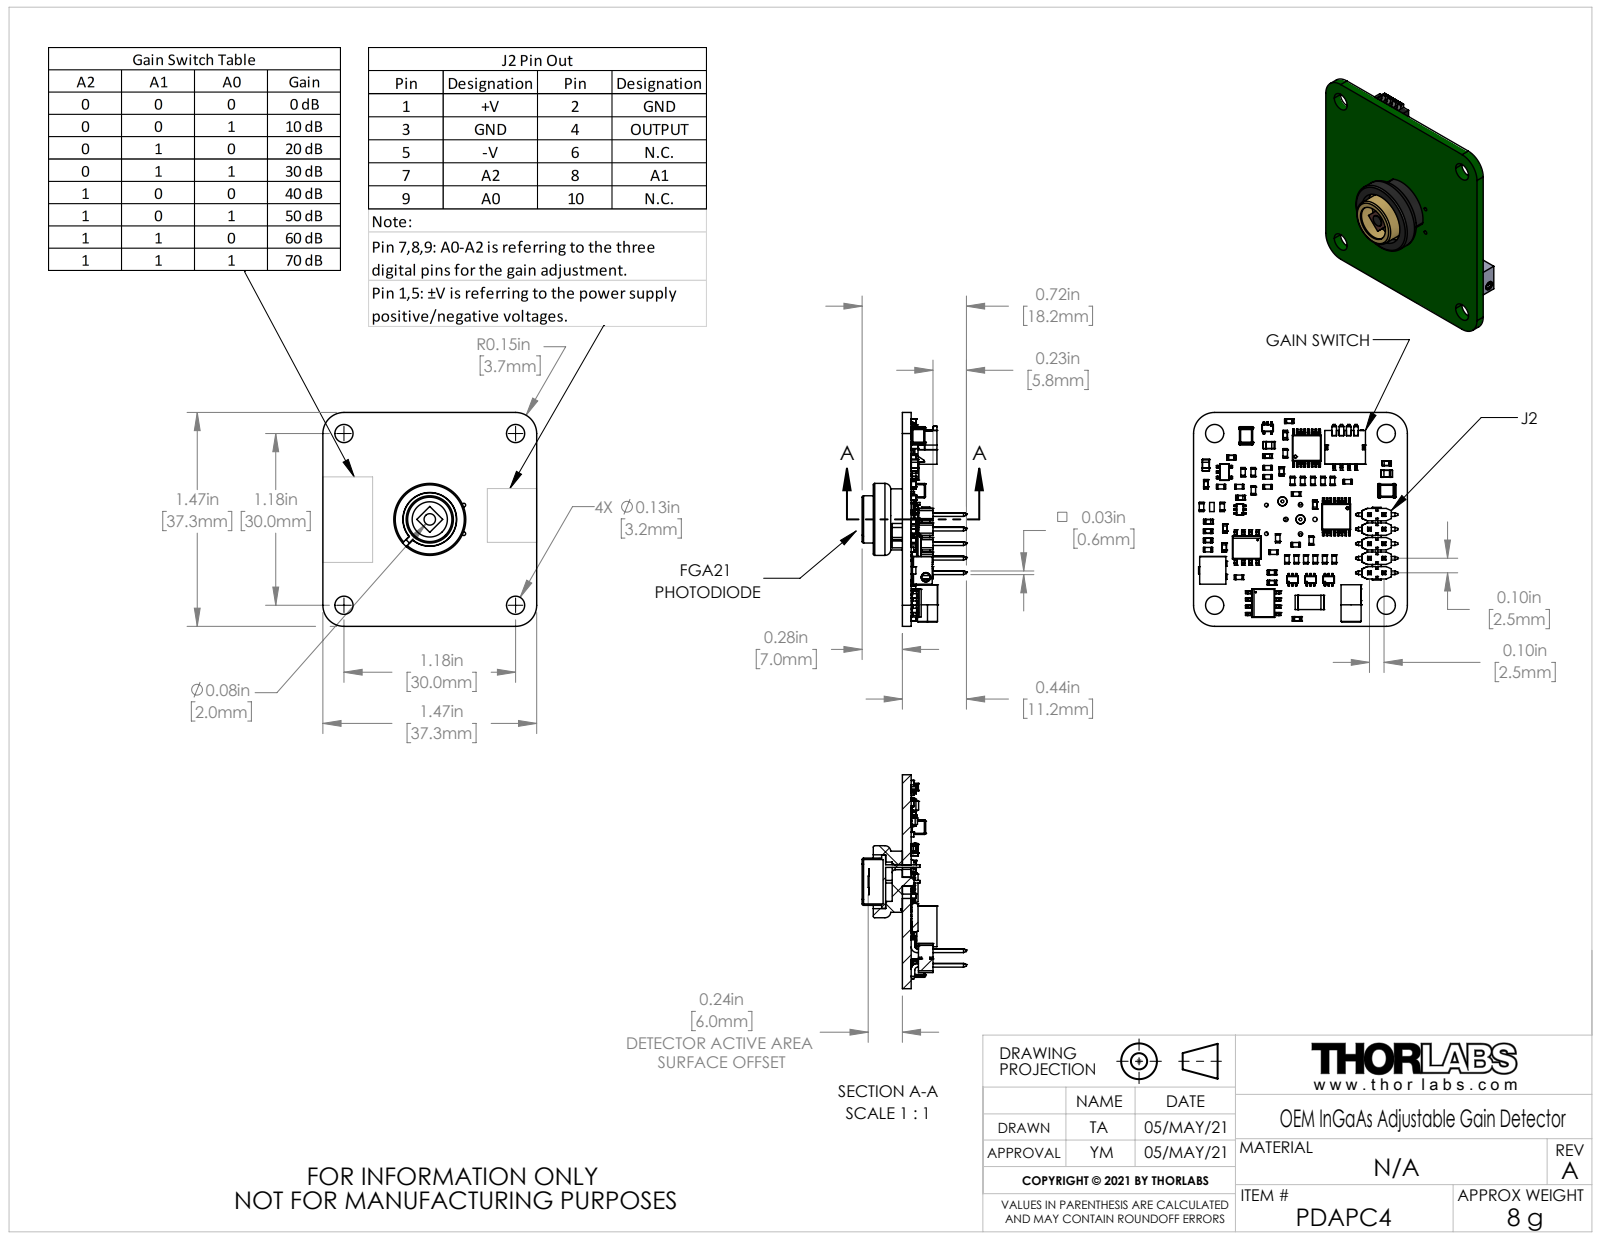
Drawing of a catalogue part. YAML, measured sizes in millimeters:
part_name: "TTN239793-E0W"
step_written_by: "SolidWorks 2018 (AUTOMOTIVE_DESIGN)"
units: millimeters
bodies: {solids: 76, faces: 4206, planar: 2902, cylindrical: 1038, other: 266}
overall_size: [37.3, 37.3, 18.2]
volume: 3160
surface_area: 5875
round_holes:
  - {diameter: 0.2, count: 5}
  - {diameter: 0.8, count: 4}
  - {diameter: 3.2, count: 4}
  - {diameter: 0.9, count: 3}
  - {diameter: 0.5, count: 2}
  - {diameter: 0.6, count: 2}
  - {diameter: 1.6, count: 2}
  - {diameter: 1, count: 1}
  - {diameter: 1.2, count: 1}
  - {diameter: 1.6, count: 1}
  - {diameter: 2.4, count: 1}
  - {diameter: 2.9, count: 1}
round_bosses_or_shafts:
  - {diameter: 1.5, count: 3}
  - {diameter: 0.5, count: 3}
  - {diameter: 12.6, count: 1}
  - {diameter: 10.7, count: 1}
  - {diameter: 9.3, count: 1}
  - {diameter: 8.3, count: 1}
  - {diameter: 3.5, count: 1}
  - {diameter: 2.3, count: 1}
partial_cylinders:
  - {radius: 0.1, count: 59}
  - {radius: 0.2, count: 54}
  - {radius: 0.3, count: 10}
  - {radius: 0.4, count: 8}
  - {radius: 0.8, count: 8}
  - {radius: 0.3, count: 6}
  - {radius: 0.1, count: 4}
  - {radius: 3.7, count: 4}
face_to_face_distances: [1.5, 2.5, 5.1, 4.5, 3.3, 2.9, 37.3, 7.8, 1.6, 1.8]
hole_center_spacings: [2.5, 3.6, 5.1, 5.7, 13.8, 7.6, 8, 12.2]
